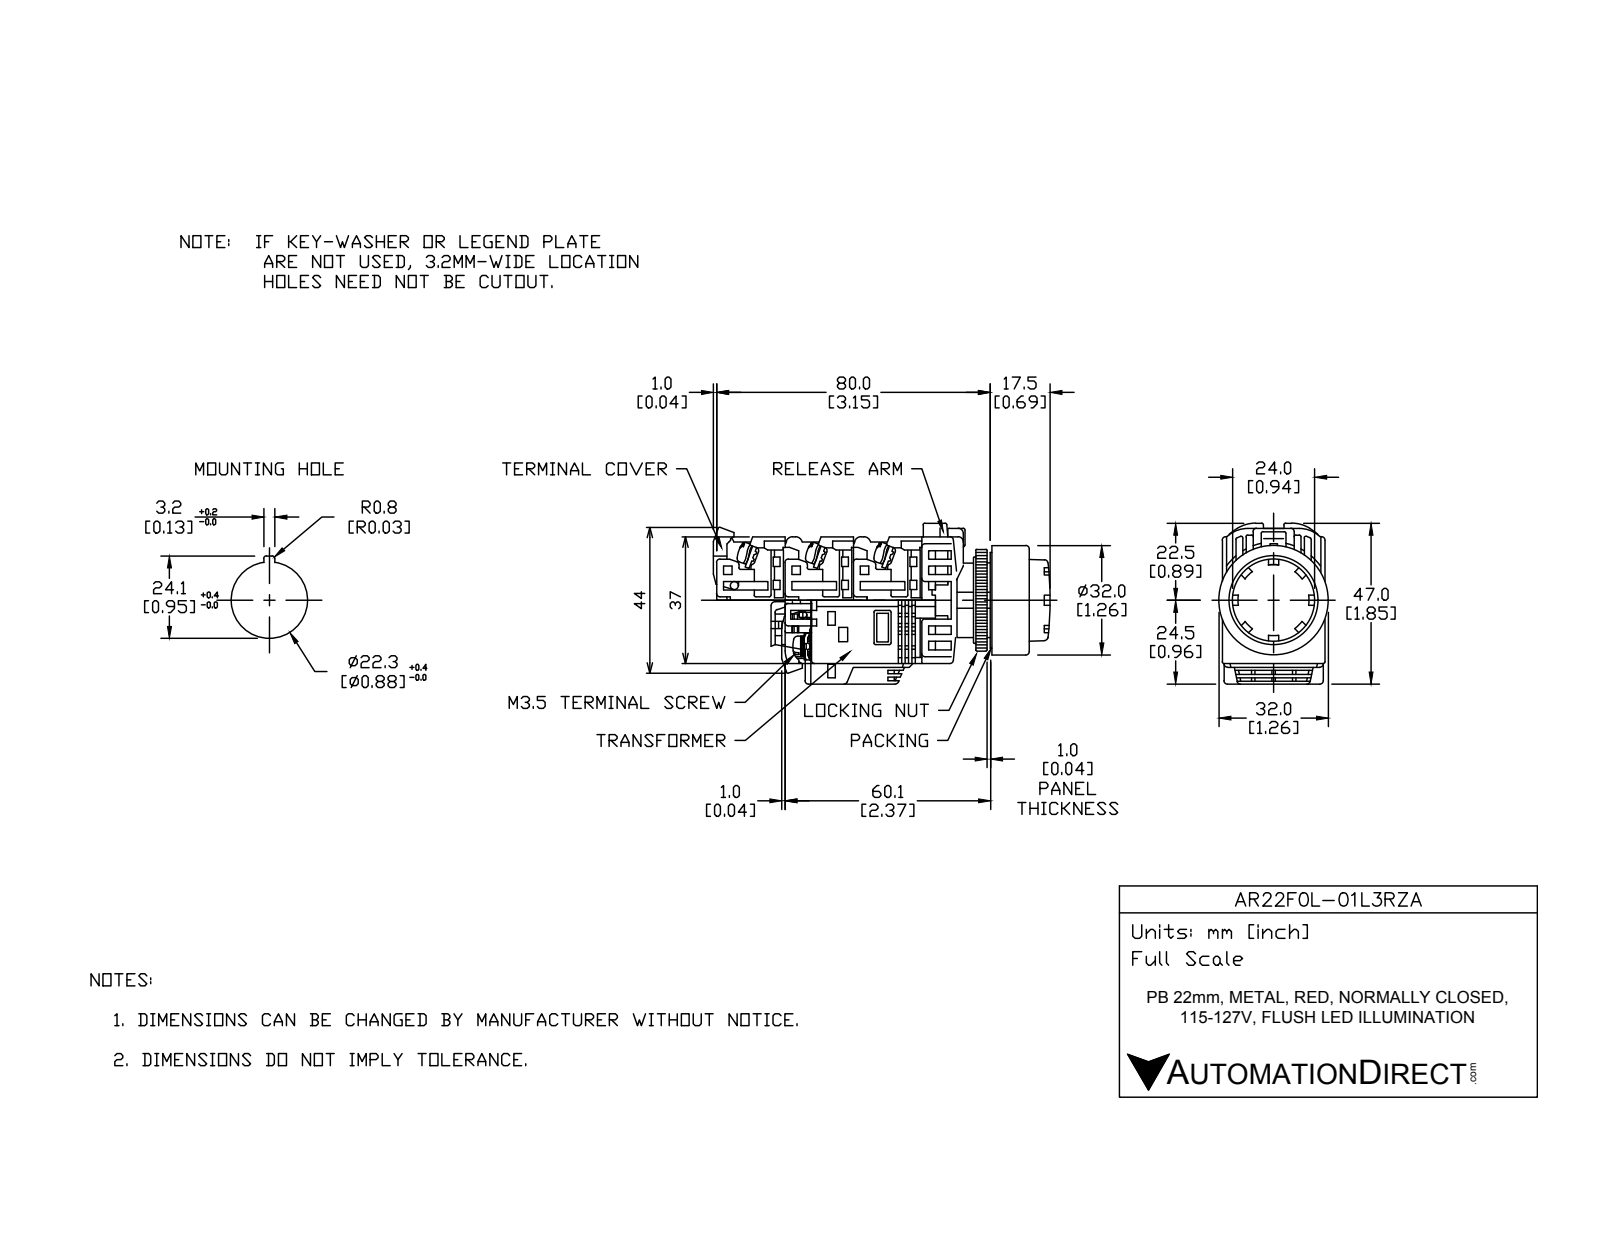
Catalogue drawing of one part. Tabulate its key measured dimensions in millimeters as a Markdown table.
| quantity | value |
| --- | --- |
| part name | AR22F0L-01L3RZA |
| STEP written by | SolidWorks 2017 (AUTOMOTIVE_DESIGN) |
| units | millimeters |
| bodies | 16 solids, 451 faces (317 planar, 99 cylindrical, 35 other) |
| overall size | 72.75 × 43.81 × 32 |
| volume | 47 521 mm³ |
| surface area | 25 721 mm² |
| round holes (diameter × count) | 21.8 × 1, 22 × 1, 25 × 1, 31 × 1 |
| round bosses / shafts (diameter × count) | 5 × 4, 32 × 1, 30.5 × 1, 29.8 × 1, 24 × 1, 23.8 × 1, 21.75 × 1, 17 × 1 |
| partial cylindrical surfaces (radius × count) | 0.5 × 32, 1.75 × 8, 5 × 4, 4 × 2, 16.59 × 1, 17.59 × 1 |
| main face-to-face distances | 1, 18, 29, 20, 28.5, 3, 2, 21, 0.35, 7.5 |
